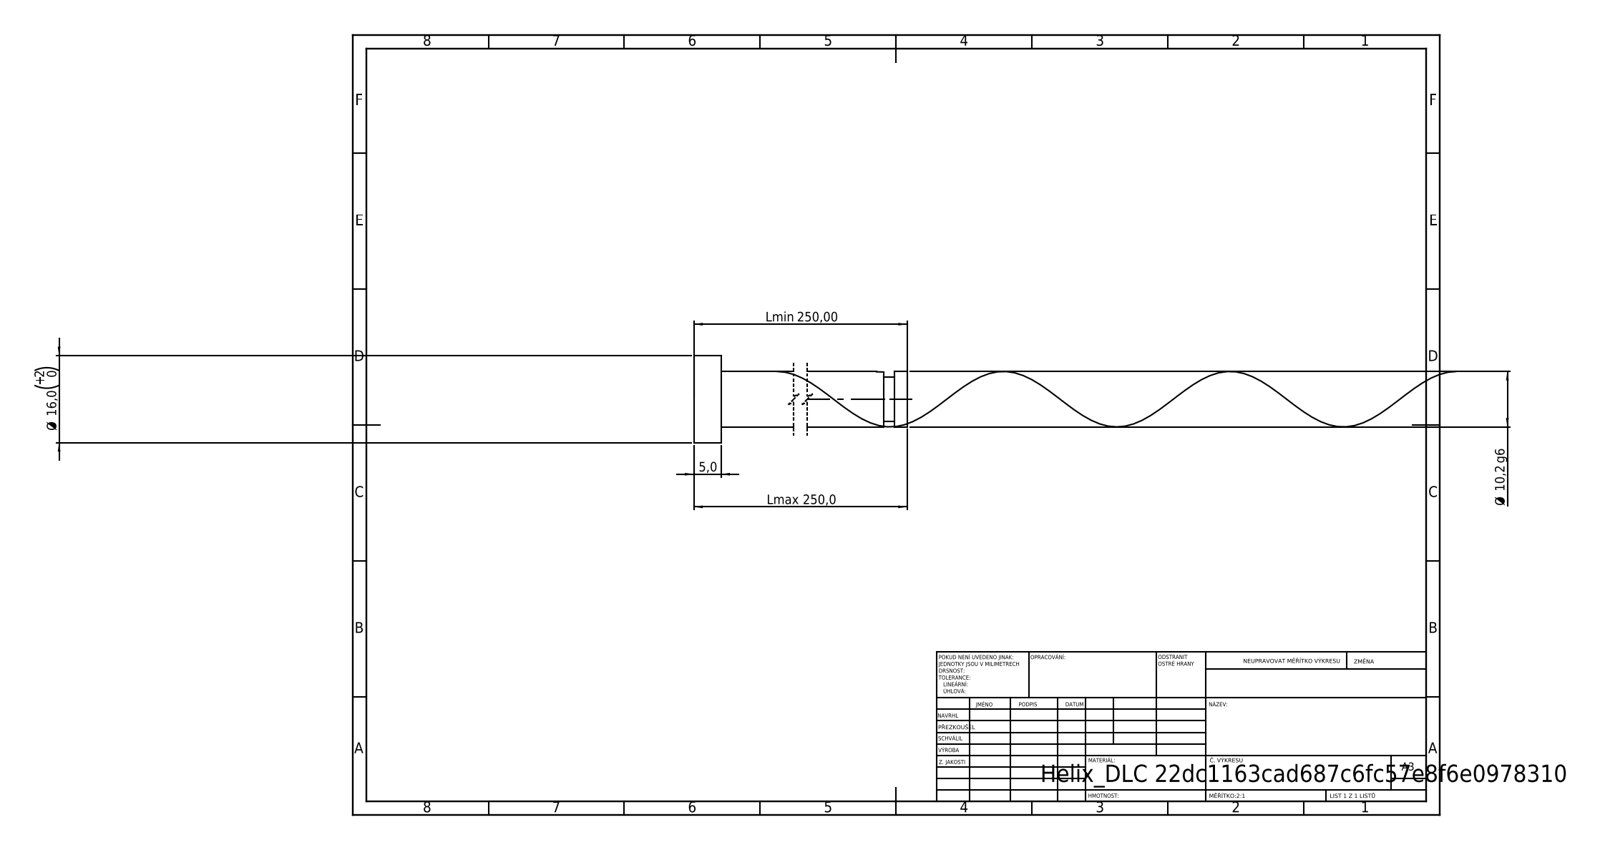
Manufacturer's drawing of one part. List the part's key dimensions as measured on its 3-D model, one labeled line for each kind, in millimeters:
STEP written by: SolidWorks 2019 (CONFIG_CONTROL_DESIGN)
Units: millimetres
Bodies: 1 solid, 21 faces (6 planar, 14 cylindrical, 1 other)
Overall size (bounding box): 250 × 16 × 16
Volume: 20 769 mm³ · Surface area: 8 717 mm²
Round bosses / shafts (diameter × count): ⌀16 ×1, ⌀10.2 ×1, ⌀8.16 ×1
Main face-to-face distances: 5, 250, 245, 247.69, 242.69, 2.31, 245.65, 240.65, 2.04, 4.35
